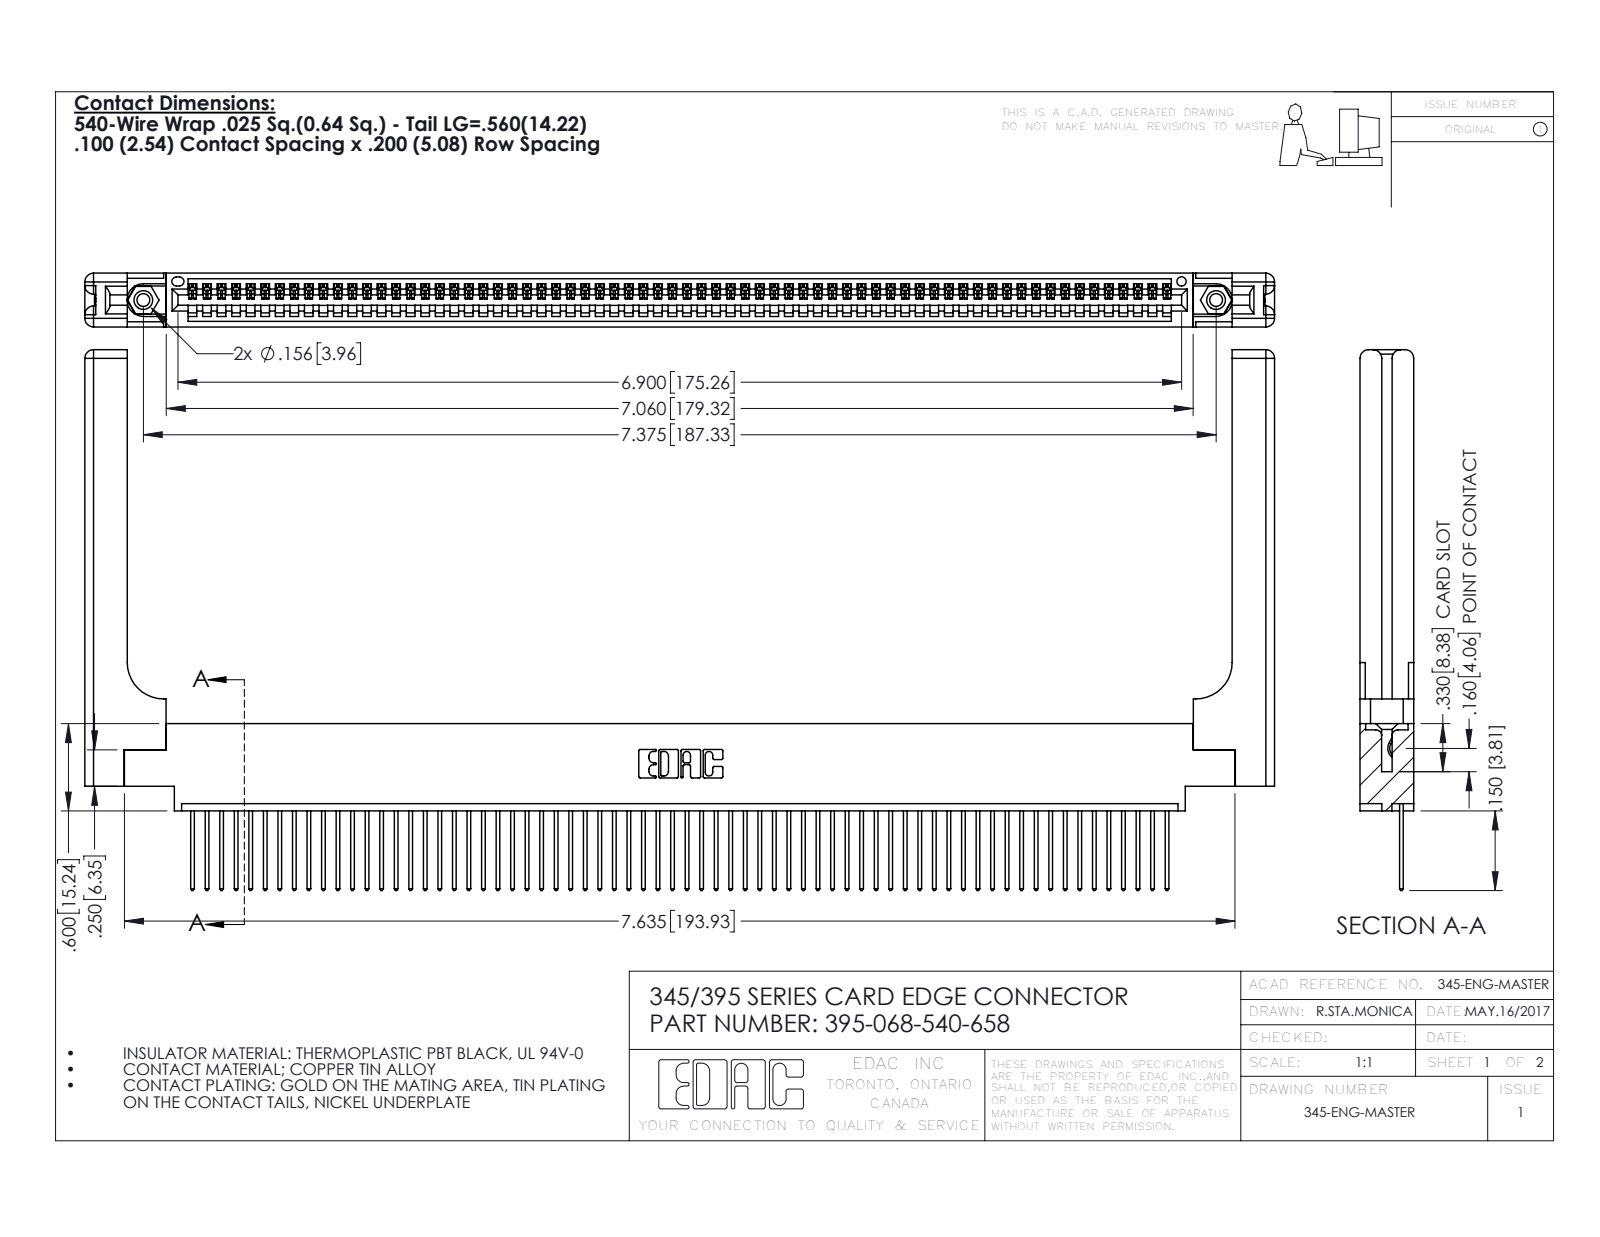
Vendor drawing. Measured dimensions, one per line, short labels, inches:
name: 345-292-001_345-293-140; 345 Part_0.170 Offset - 0.156 Dia-TH; 395-068-540-658; 345-250-001_345-250-001-102 (+1 more)
written by: SolidWorks 2016 (CONFIG_CONTROL_DESIGN)
unit: in
bodies: 73 solids, 4330 faces (2952 planar, 1318 cylindrical, 60 other)
size: 8.179 × 3.717 × 0.37
volume: 1.735 in³; area: 51.03 in²
holes: 2× ⌀0.089, 2× ⌀0.125, 2× ⌀0.156, 1× ⌀0.064
bosses: 2× ⌀0.155
rounds: 136× R0.006, 136× R0.01, 22× R0.01, 16× R0.06, 6× R0.007, 6× R0.031, 3× R0.026, 2× R0.03
face distances: 0.072, 0.298, 0.37, 0.098, 0.272, 0.025, 0.2, 0.225, 0.148, 0.15
hole spacings: 0.27, 7.139, 7.375
